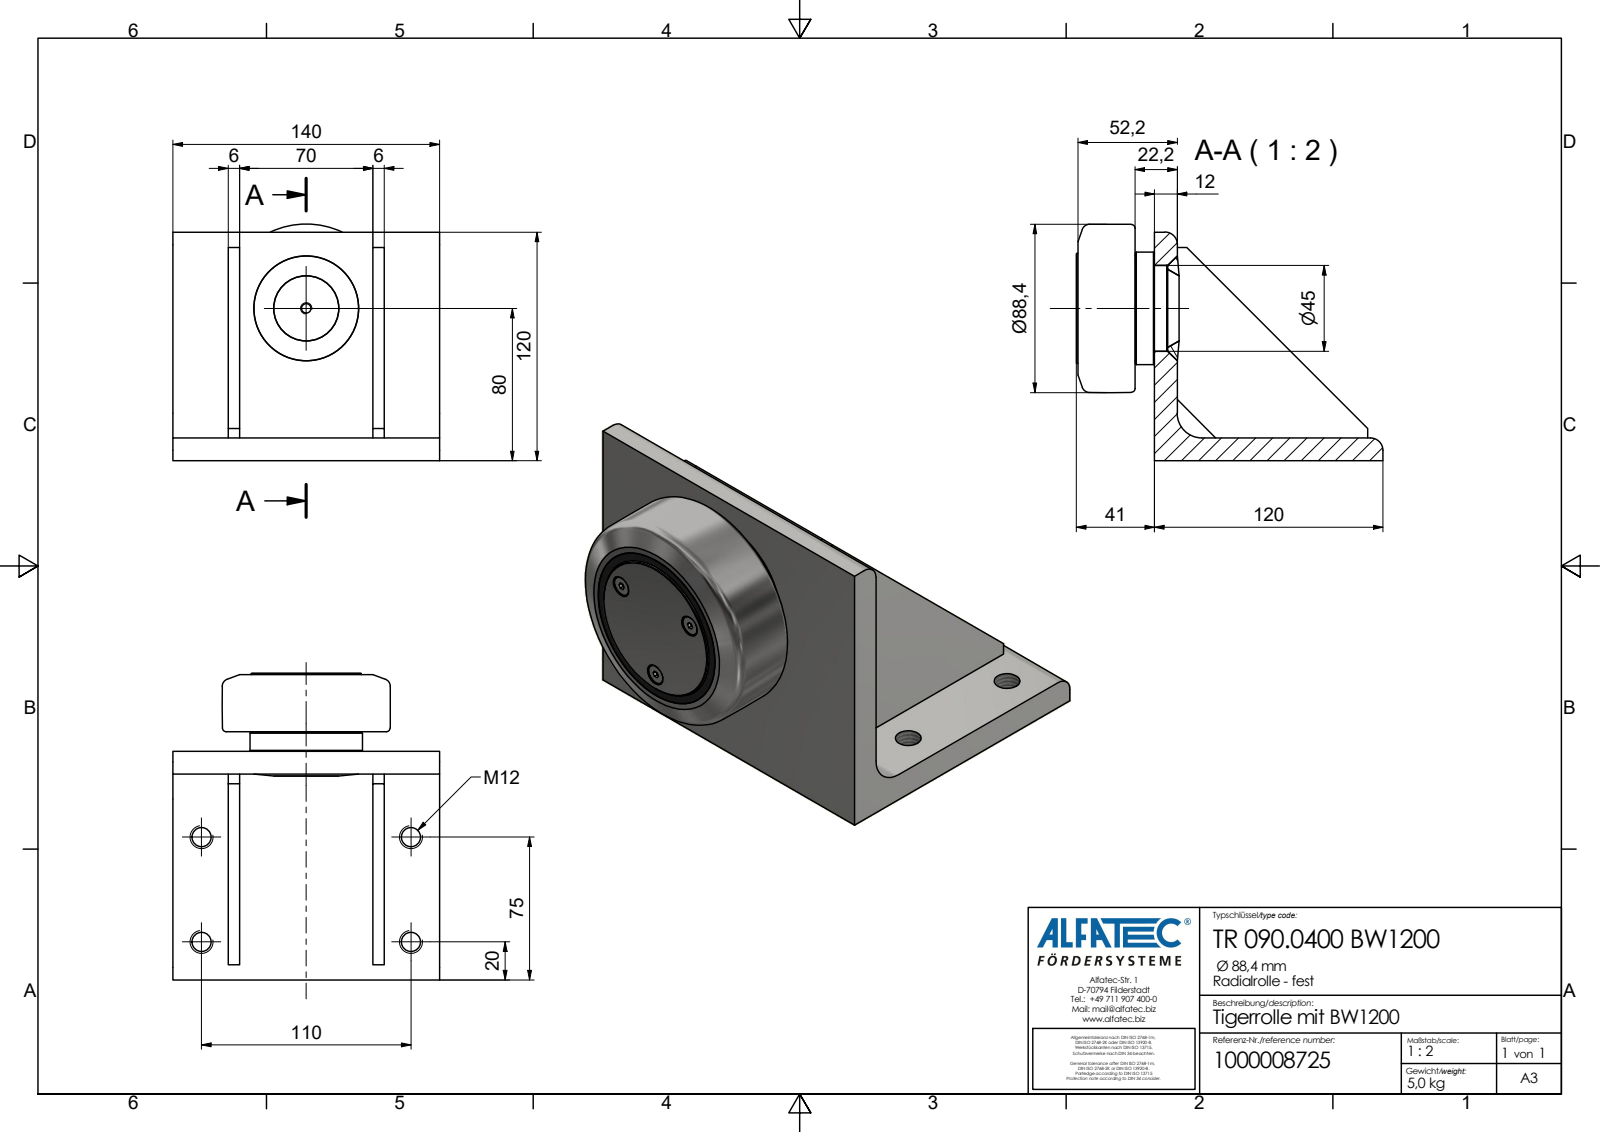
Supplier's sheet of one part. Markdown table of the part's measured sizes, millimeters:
| quantity | value |
| --- | --- |
| part name | TR 090.0400 BW1200_Kontur |
| STEP written by | Autodesk Inventor 2020 (AP242_MANAGED_MODEL_BASED_3D_ENGINEERING_MIM_LF) |
| units | millimeters |
| bodies | 1 solid, 81 faces (53 planar, 17 cylindrical, 11 other) |
| overall size | 161 × 140 × 124.2 |
| volume | 655 306 mm³ |
| surface area | 110 390 mm² |
| round holes (diameter × count) | 10.11 × 4, 8.6 × 3, 4.92 × 1 |
| round bosses / shafts (diameter × count) | 7.8 × 3, 59 × 1, 57.8 × 1, 55.3 × 1 |
| partial cylindrical surfaces (radius × count) | 6.5 × 2, 13 × 1 |
| main face-to-face distances | 12, 76, 6, 29, 35, 105, 111, 82, 70, 10.2 |
| hole center spacings | 22, 38.1, 55, 110, 122.98 |
